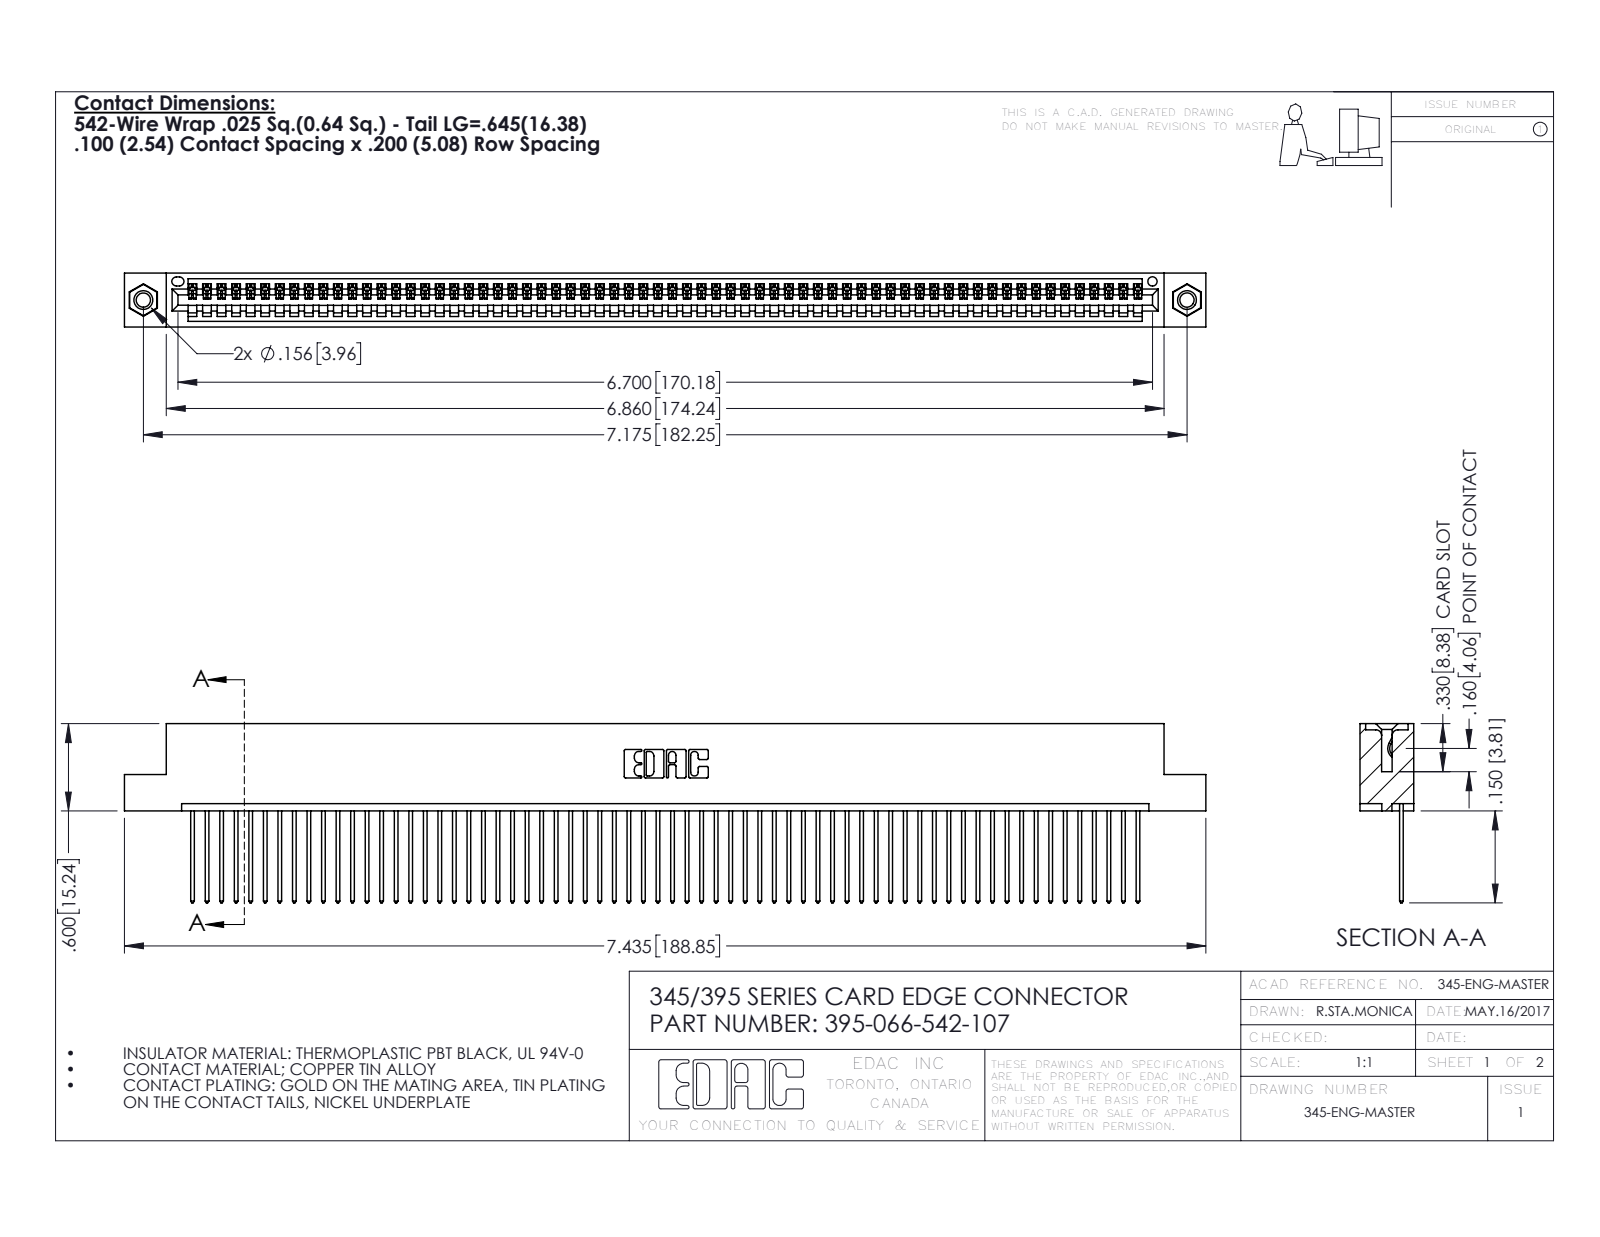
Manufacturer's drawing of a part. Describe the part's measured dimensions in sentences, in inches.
The part is named "395-066-542-107; 345 Part_Flush Mounting Lugs - 0.156 Dia-TI; 345-250-001_345-250-005-103; 345-292-001_345-293-142". Its 3-D file was written by "SolidWorks 2016 (CONFIG_CONTROL_DESIGN)". It is 69 solids with 4014 faces: 2752 planar, 1246 cylindrical and 16 other. Overall it measures 7.435 by 1.232 by 0.37 inches. Its volume is 1.115 cubic inches and its surface area 39.62 square inches. Round holes: 2 of diameter 0.098, 2 of diameter 0.125, 2 of diameter 0.156, 1 of diameter 0.064. Round bosses or shafts: 2 of diameter 0.155. Partial cylindrical surfaces (rounded edges, fillets, slot ends): 132 of radius 0.006, 132 of radius 0.01, 22 of radius 0.01, 6 of radius 0.007, 6 of radius 0.031, 3 of radius 0.026, 2 of radius 0.031, 2 of radius 0.04. The main face-to-face distances are 0.072, 0.298, 0.098, 0.272, 0.025, 0.37, 0.2, 0.225, 0.149, 0.072. The hole center spacings are 0.27, 6.939, 7.175.
